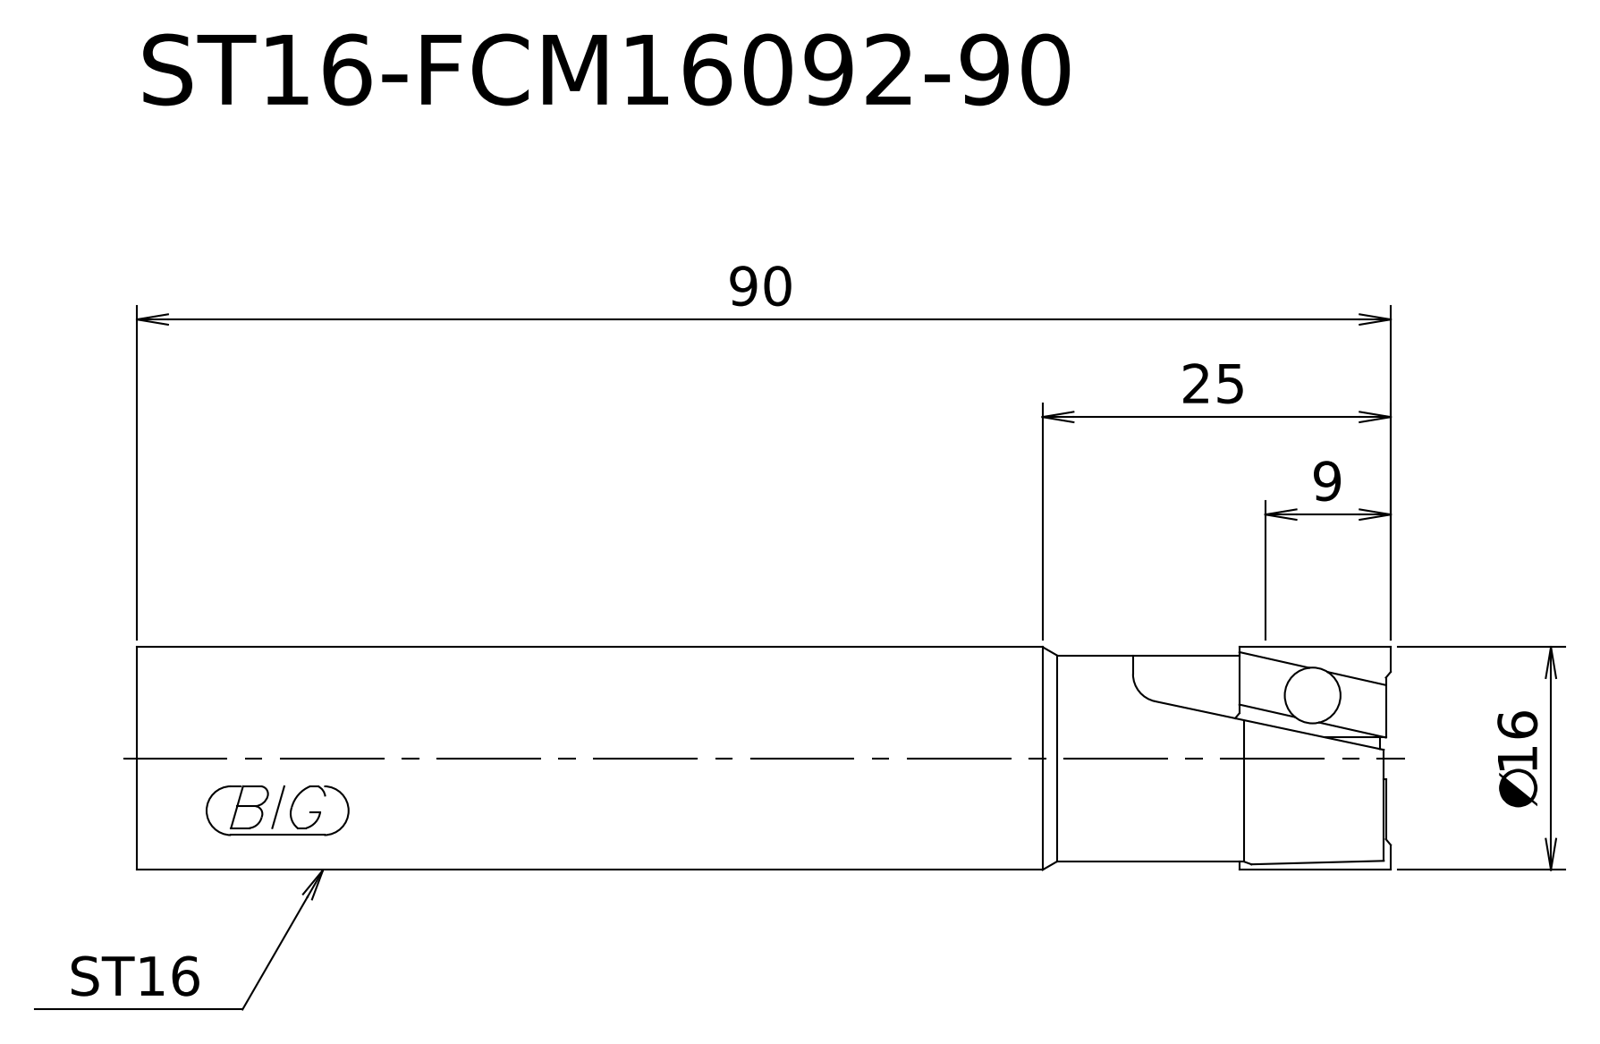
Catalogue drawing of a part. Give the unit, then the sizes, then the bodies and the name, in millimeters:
Units: millimetres
Overall size (bounding box): 90 × 16 × 16
Round bosses / shafts (diameter × count): ⌀16 ×1, ⌀14.8 ×1
Main face-to-face distances: 90, 10.86, 79.14
Volume: 17 700 mm³ · Surface area: 4 911 mm²
Bodies: 1 solid, 7 faces (3 planar, 3 cylindrical, 1 other)
STEP written by: Kubotek KeyCreator V8.5.1 (14335) (CONFIG_CONTROL_DESIGN)
